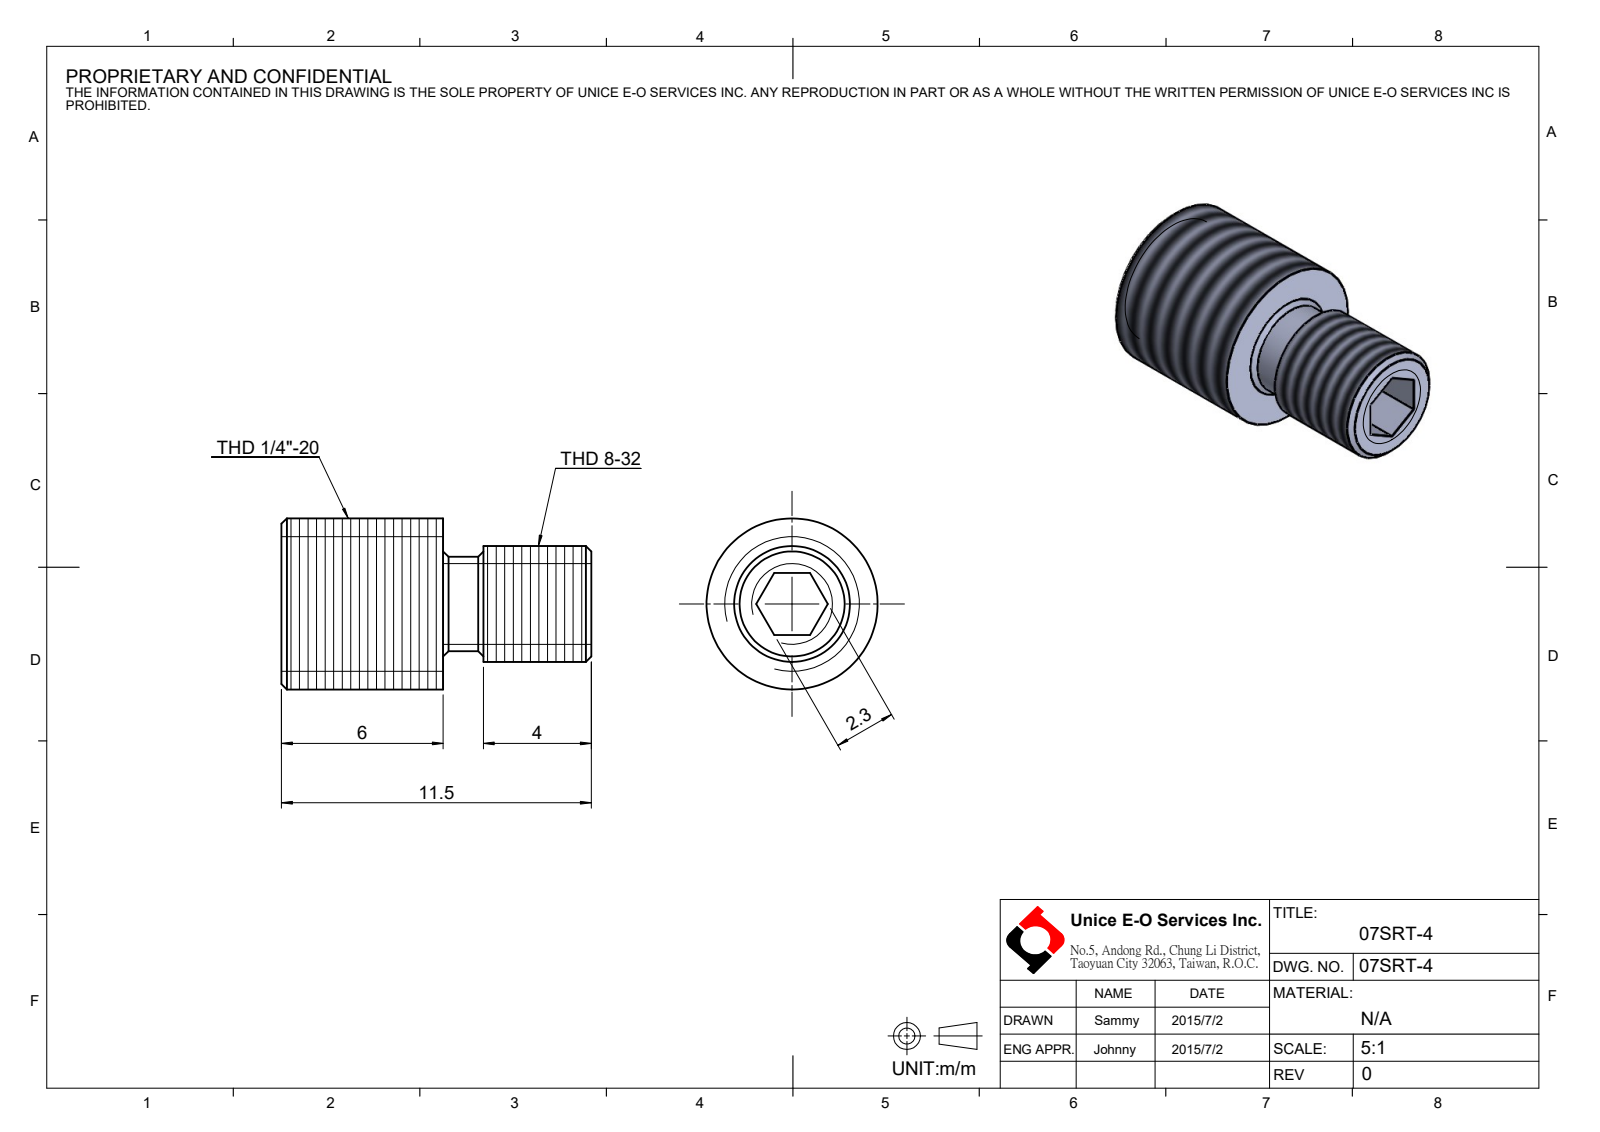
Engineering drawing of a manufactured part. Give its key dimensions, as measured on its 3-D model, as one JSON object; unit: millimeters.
{"part_name": "07SRT-4", "step_written_by": "SolidWorks 2016 (CONFIG_CONTROL_DESIGN)", "units": "millimeters", "bodies": {"solids": 1, "faces": 32, "planar": 18, "cylindrical": 6, "other": 8}, "overall_size": [11.5, 6.35, 6.35], "volume_mm3": 235, "surface_area_mm2": 305, "round_bosses_or_shafts": [[6.35, 1], [4.3, 1], [3.5, 1]], "face_to_face_distances": [2.3, 6, 3, 5.5, 8.5, 11.5, 2.5, 7.5, 4.5, 1.5]}
